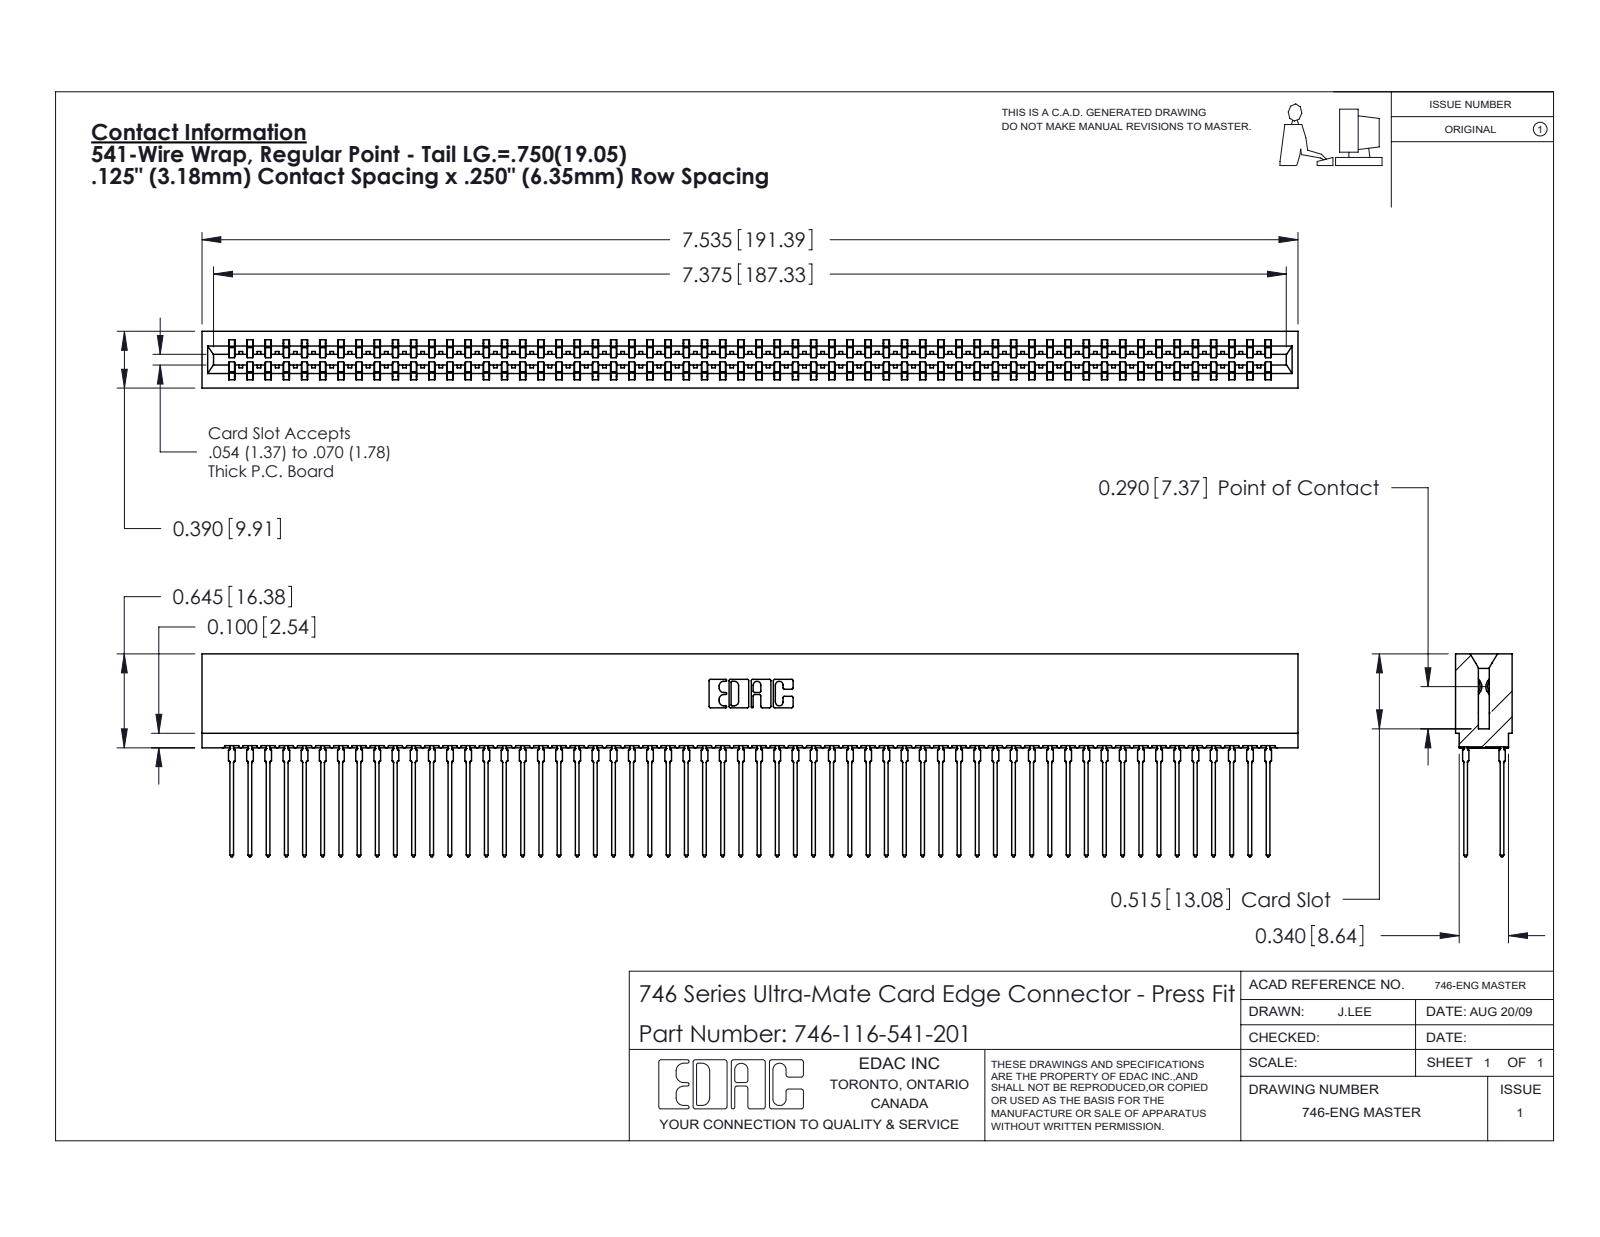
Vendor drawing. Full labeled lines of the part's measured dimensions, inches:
Part name (STEP PRODUCT): 746 Part_.515 Slot Depth - 01; 746-116-541-201; 746-292-001_541
STEP written by: SolidWorks 2020 (CONFIG_CONTROL_DESIGN)
Units: inches
Bodies: 117 solids, 10479 faces (5391 planar, 2072 cylindrical, 3016 other)
Overall size (bounding box): 7.535 × 1.394 × 0.39
Volume: 1.284 in³ · Surface area: 57.5 in²
Partial cylindrical surfaces — rounded edges, fillets, slot ends (radius × count): R0.021 ×232, R0.015 ×59, R0.01 ×22, R0.005 ×8, R0.011 ×8, R0.007 ×6, R0.031 ×6, R0.026 ×3
Main face-to-face distances: 0.057, 0.333, 0.25, 0.025, 0.307, 0.39, 0.083, 0.275, 0.174, 0.158
